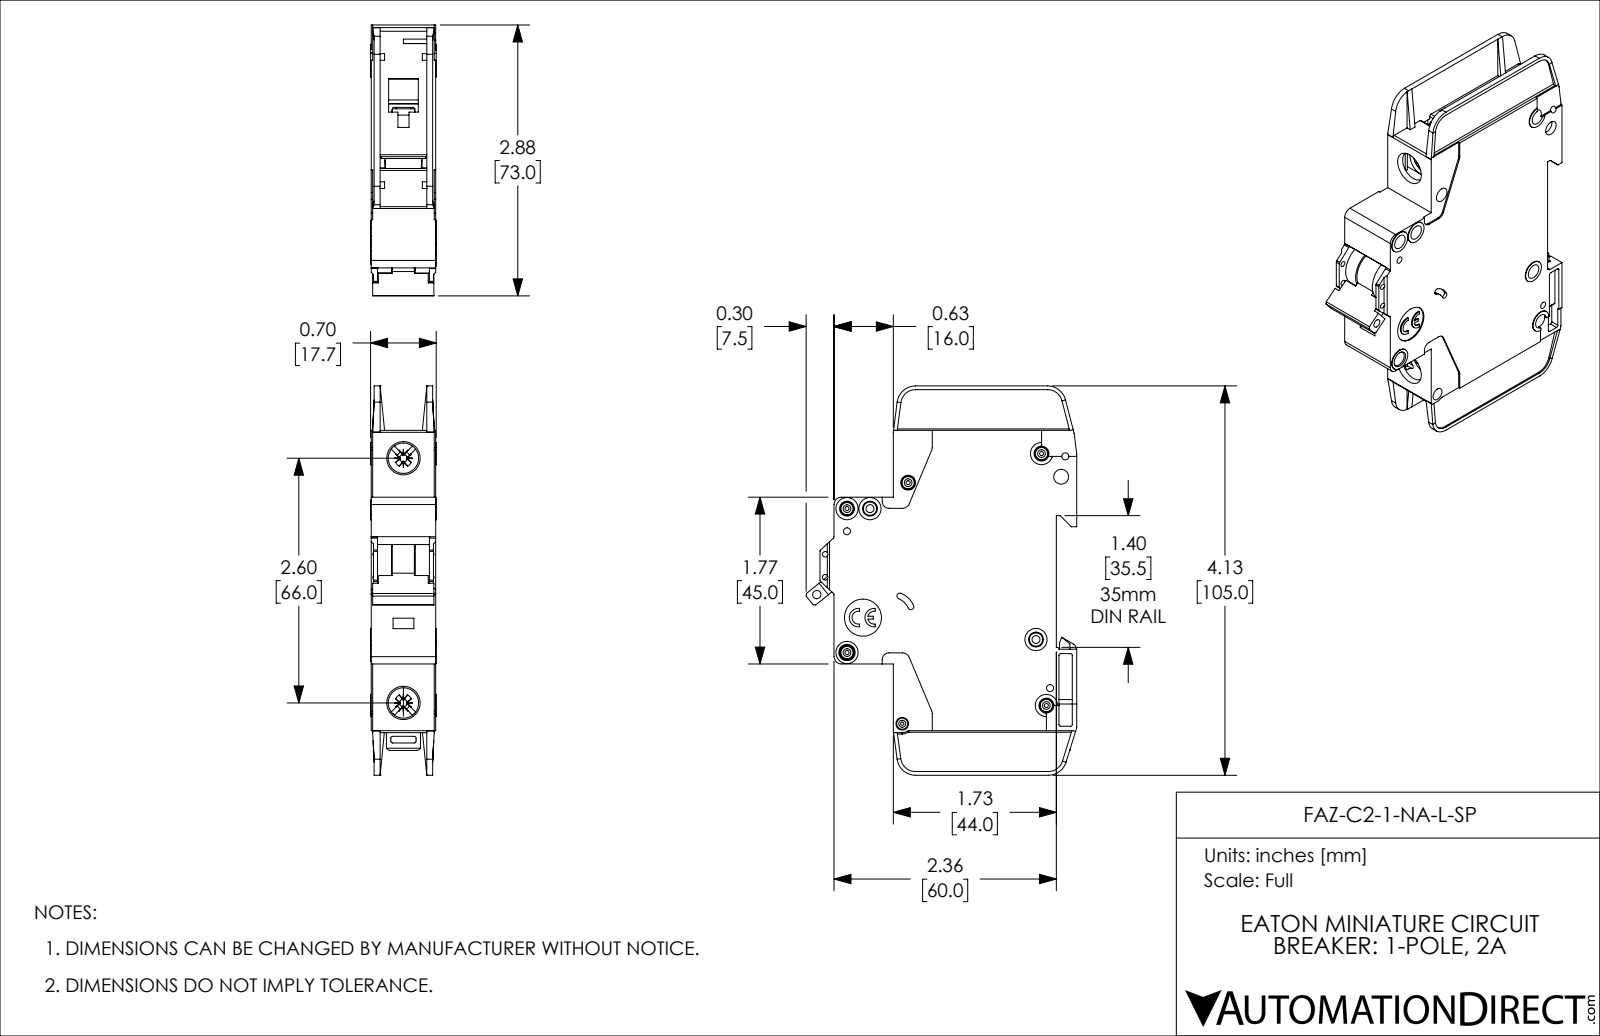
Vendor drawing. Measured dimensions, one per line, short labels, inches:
name: FAZ-C2-1-NA-L-SP
written by: SolidWorks 2019 (AUTOMOTIVE_DESIGN)
unit: in
bodies: 1 solid, 1127 faces (671 planar, 357 cylindrical, 99 other)
size: 4.134 × 2.876 × 0.697
volume: 4.682 in³; area: 41.01 in²
holes: 8× ⌀0.157, 5× ⌀0.043, 4× ⌀0.075, 2× ⌀0.059, 2× ⌀0.085, 2× ⌀0.323, 1× ⌀0.035, 1× ⌀0.089, 1× ⌀0.098, 1× ⌀0.134, 1× ⌀0.394
bosses: 5× ⌀0.13, 4× ⌀0.236, 2× ⌀0.118, 1× ⌀0.098
rounds: 42× R0.02, 10× R0.016, 10× R0.039, 8× R0.079, 5× R0.197, 4× R0.008, 4× R0.026, 4× R0.043
face distances: 0.047, 0.685, 0.591, 0.638, 0.094, 0.543, 0.016, 0.031, 0.496, 0.575
hole spacings: 0.244, 0.537, 0.87, 0.189, 0.199, 0.204, 0.221, 0.24
